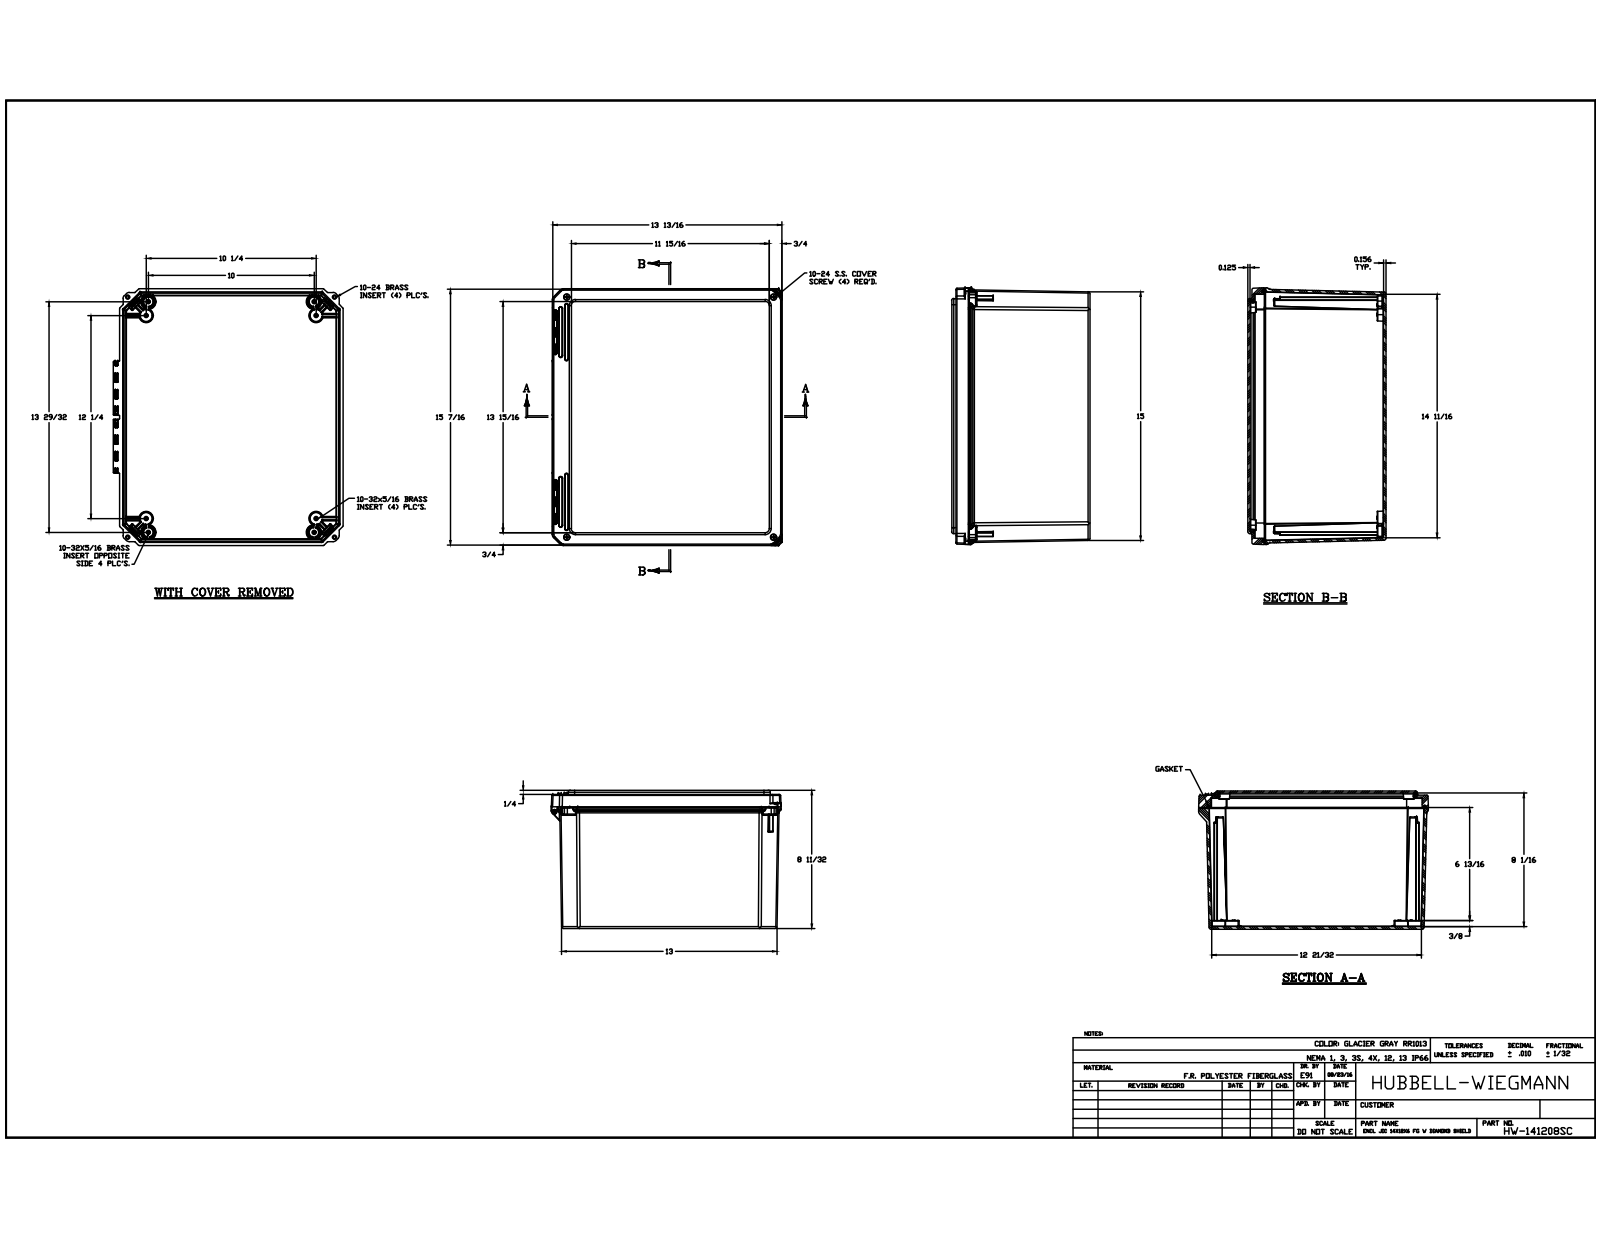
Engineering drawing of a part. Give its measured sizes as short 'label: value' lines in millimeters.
name: HW-141208SC; DS141208BOX; BRASS INSERT-(; BRASS INSERT-(_1 (+5 more)
written by: Autodesk Inventor 2017 (CONFIG_CONTROL_DESIGN)
unit: mm
bodies: 23 solids, 2150 faces (730 planar, 778 cylindrical, 642 other)
size: 393.62 × 352.15 × 211.87
volume: 2 365 000 mm³; area: 1 172 000 mm²
holes: 12× ⌀3.96, 8× ⌀3.86, 4× ⌀6.4, 4× ⌀6.43, 2× ⌀5.56, 2× ⌀5.77, 2× ⌀7.94, 1× ⌀3.48
bosses: 12× ⌀6.25, 4× ⌀11.43, 4× ⌀5.05, 2× ⌀11.05
rounds: 175× R0.25, 88× R0.13, 49× R0.51, 43× R0.76, 28× R1.59, 24× R0.76, 24× R2.29, 24× R2.44
face distances: 3.96, 3.17, 207.91, 211.87, 4.07, 4.03, 208.7, 204.74, 6.35, 3.18
hole spacings: 40.23, 285.72, 290.19, 21.02, 32.54, 258.01, 311.15, 317.23
